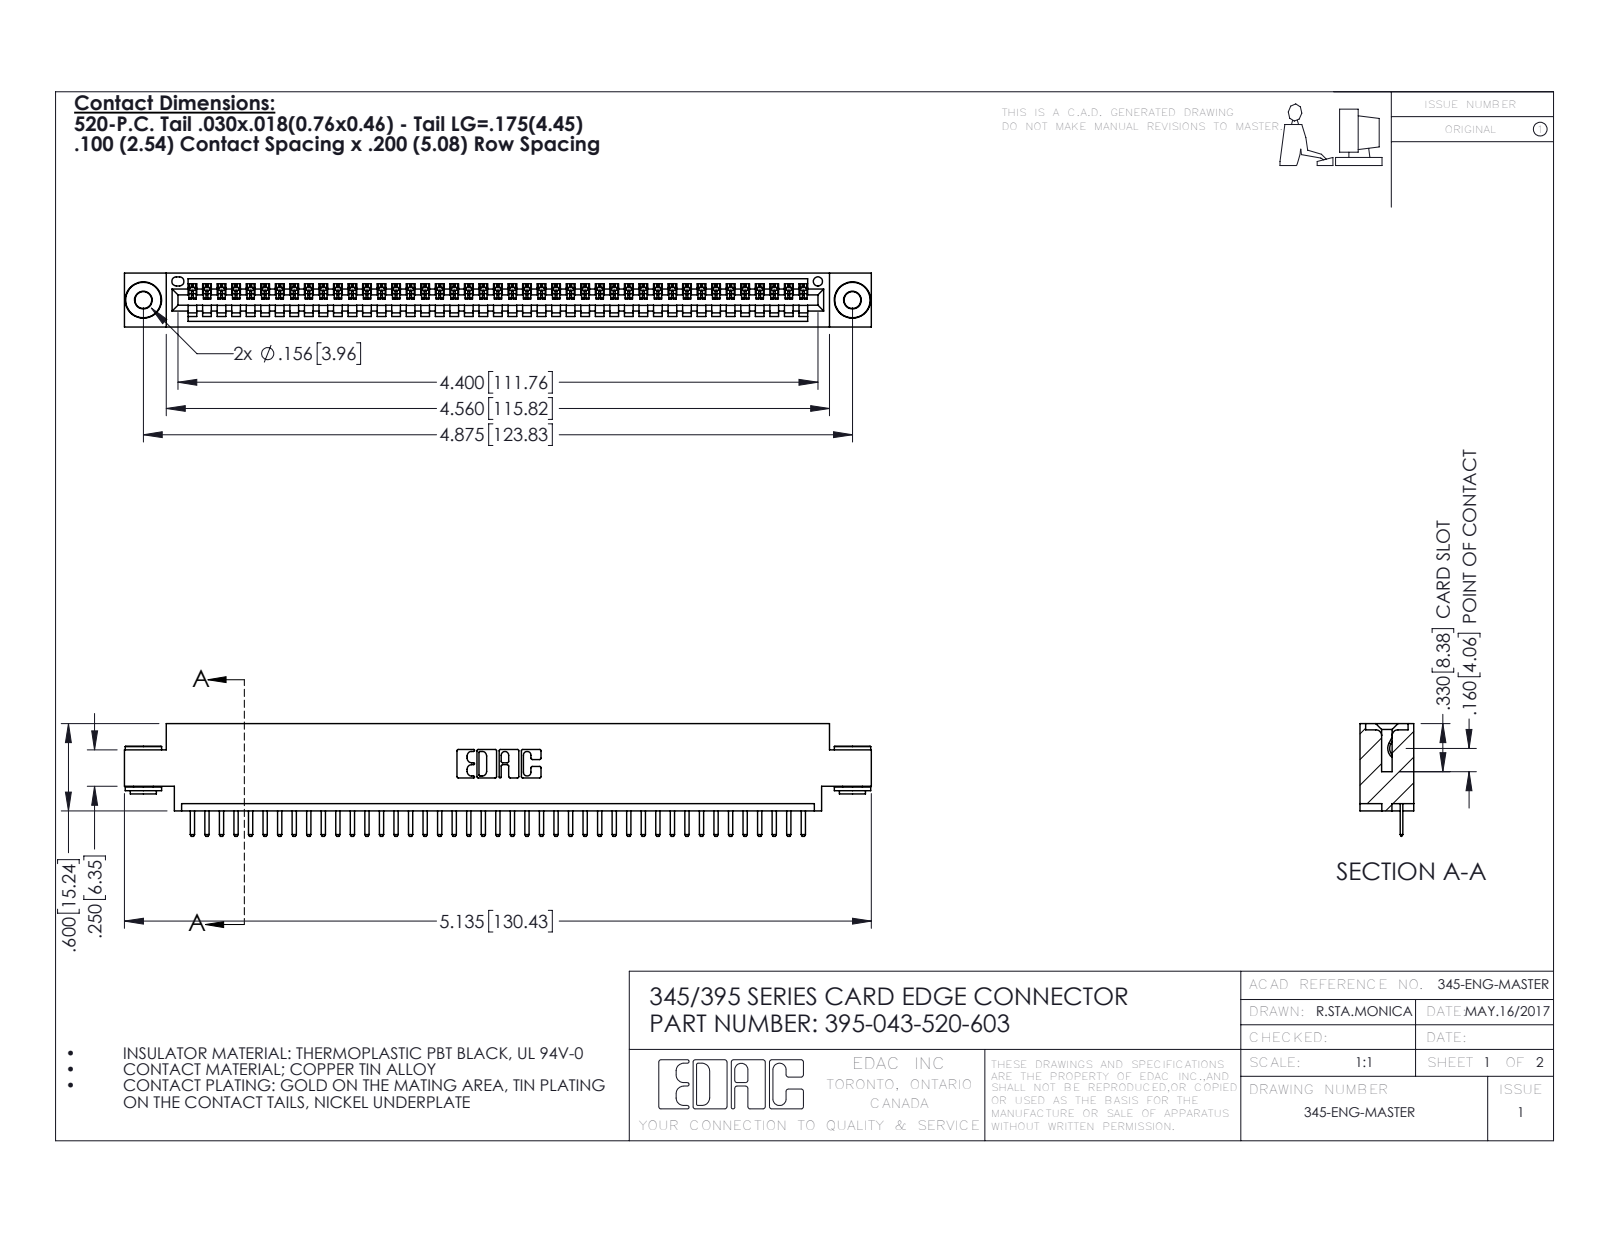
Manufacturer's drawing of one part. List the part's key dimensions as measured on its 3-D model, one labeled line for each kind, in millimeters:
Part name (STEP PRODUCT): 345-250-002_345-250-002-102; 395-043-520-603; 345-292-001_345-293-120; 345 Part_0.170 Offset - 0.156 Dia-TH
STEP written by: SolidWorks 2016 (CONFIG_CONTROL_DESIGN)
Units: millimetres
Bodies: 46 solids, 2834 faces (1900 planar, 926 cylindrical, 8 other)
Overall size (bounding box): 130.4 × 19.7 × 9.4
Volume: 12 200 mm³ · Surface area: 16 140 mm²
Round holes (diameter × count): ⌀2.9 ×2, ⌀4 ×2, ⌀1.6 ×1
Round bosses / shafts (diameter × count): ⌀6.4 ×2, ⌀4.6 ×2, ⌀3.5 ×2
Partial cylindrical surfaces — rounded edges, fillets, slot ends (radius × count): R0.3 ×88, R0.2 ×86, R0.3 ×22, R0.2 ×6, R0.8 ×6, R0.7 ×3, R0.8 ×2, R1 ×2
Main face-to-face distances: 1.8, 7.6, 9.4, 5.1, 2.5, 6.9, 0.6, 5.7, 4.4, 1.8
Hole centre spacings: 6.9, 117.8, 123.8
